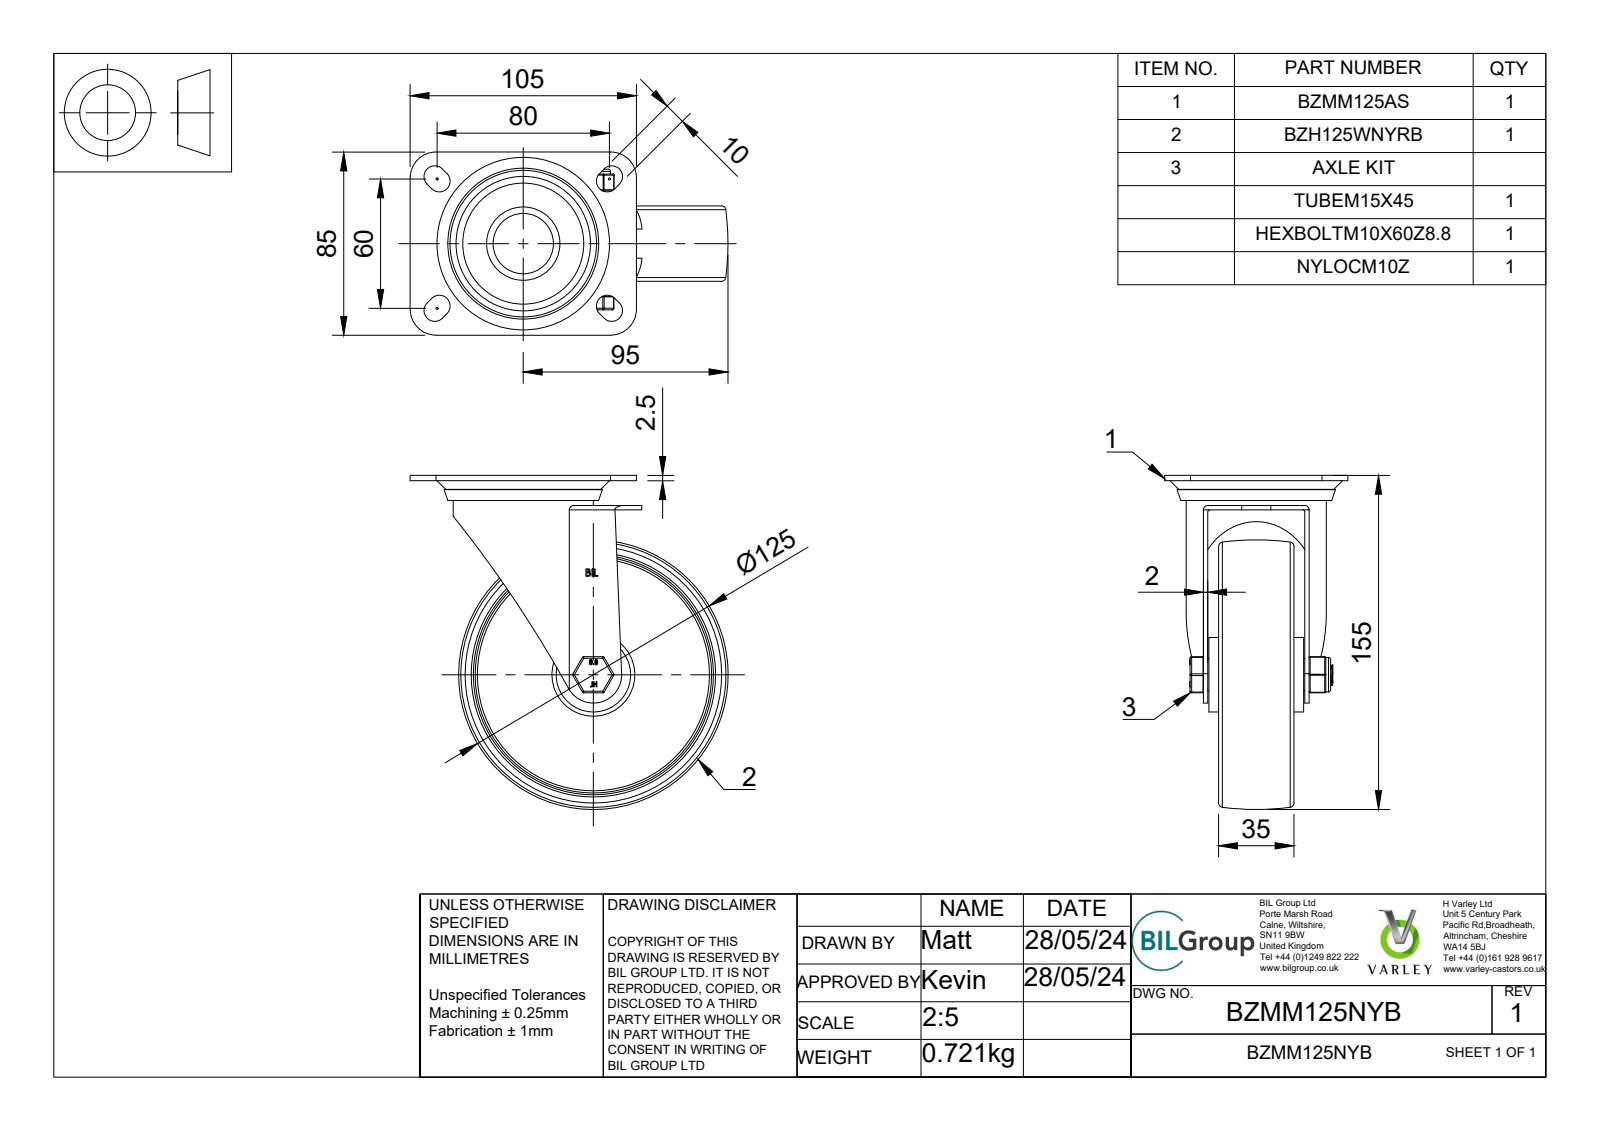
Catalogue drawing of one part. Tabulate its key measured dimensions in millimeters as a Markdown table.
| quantity | value |
| --- | --- |
| part name | BZMM125NYB v4; BZMM125AS - 2 v2; ZINC PLATED, PRESSED STEEL TOP PLATE; ZINC PLATED, PRESSED STEEL FORKS (+8 more) |
| STEP written by | Autodesk Translation Framework v13.14.0.145 (AUTOMOTIVE_DESIGN) |
| units | millimeters |
| bodies | 19 solids, 441 faces (197 planar, 147 cylindrical, 97 other) |
| overall size | 155 × 147.5 × 85 |
| volume | 273 859 mm³ |
| surface area | 121 870 mm² |
| round holes (diameter × count) | 10 × 1, 10.2 × 1, 10.3 × 1, 12 × 1, 15 × 1, 28 × 1, 61 × 1 |
| round bosses / shafts (diameter × count) | 4 × 8, 65 × 1, 49 × 1, 34.5 × 1, 34 × 1, 23 × 1, 22.75 × 1, 16 × 1 |
| partial cylindrical surfaces (radius × count) | 0.5 × 18, 0.75 × 12, 5 × 8, 1 × 4, 12 × 4, 2 × 2, 20.69 × 2, 9.38 × 1 |
| main face-to-face distances | 9, 2, 2.5, 5, 7, 4.5, 20, 18, 47, 29 |
